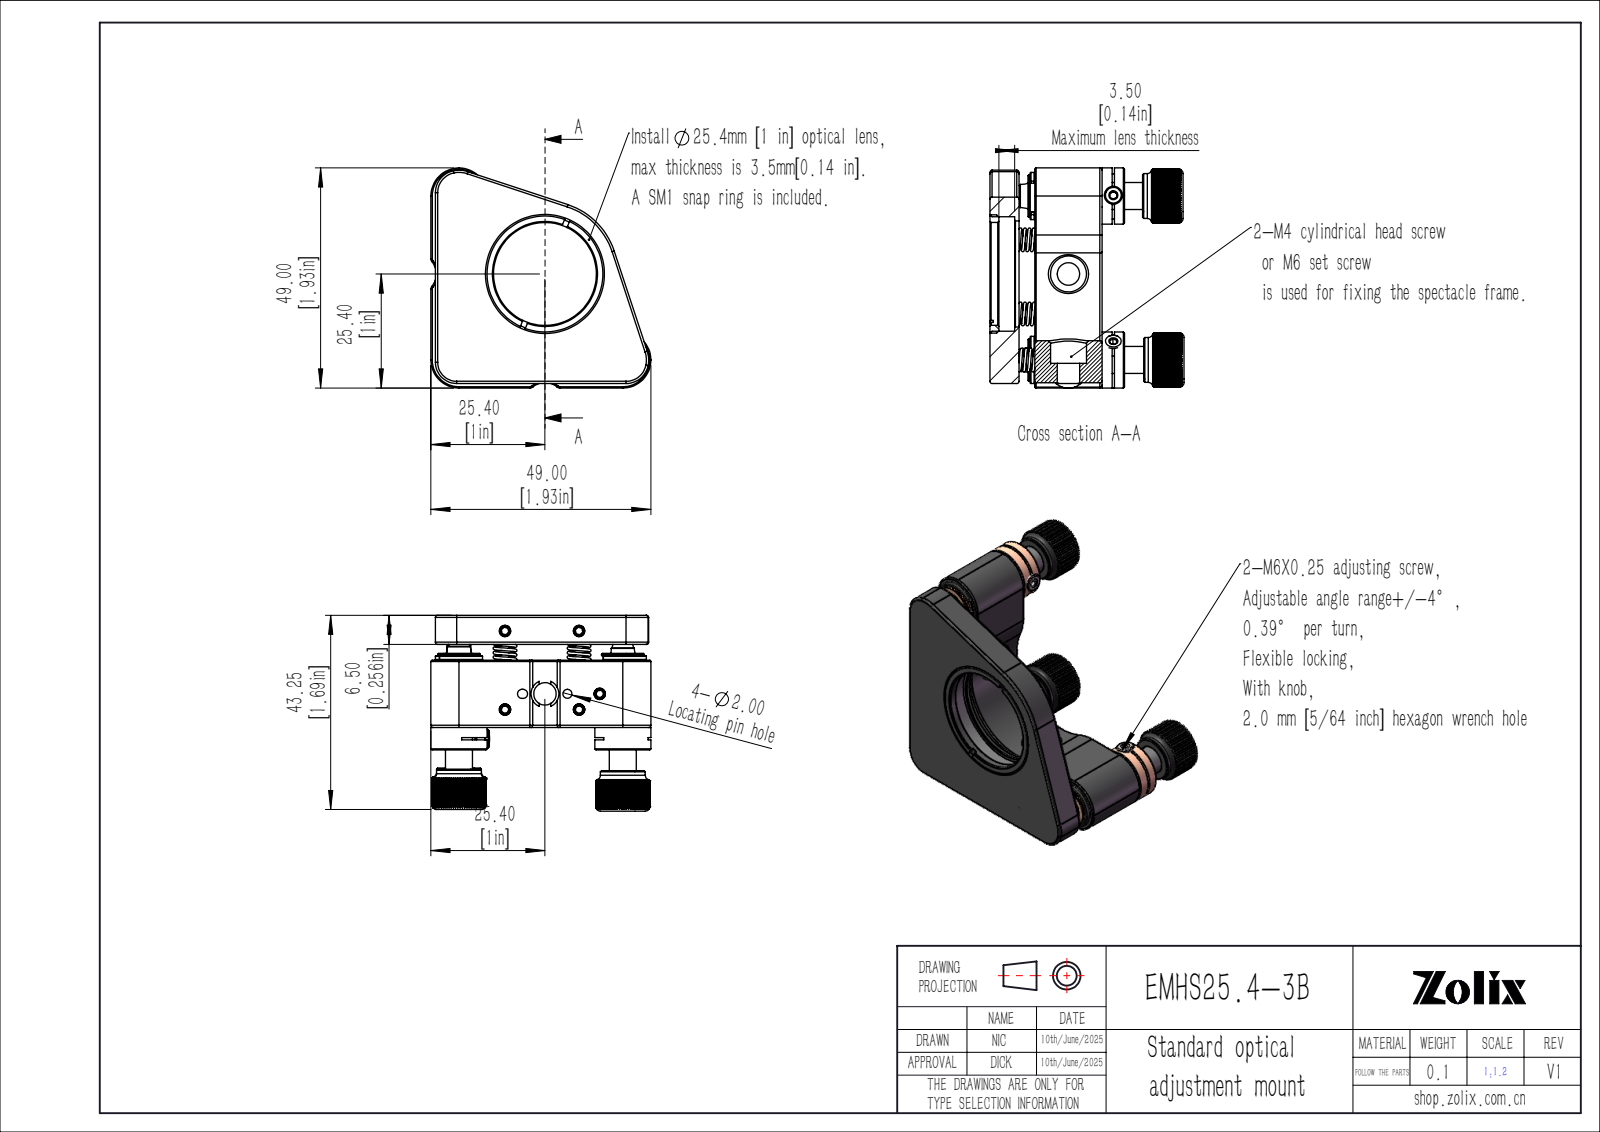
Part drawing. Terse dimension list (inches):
name: EMHS25.4-3B
written by: SolidWorks 2020 (CONFIG_CONTROL_DESIGN)
unit: in
bodies: 0 solids, 1287 faces (618 planar, 401 cylindrical, 268 other)
size: 1.929 × 1.929 × 1.717
holes: 5× ⌀0.236, 4× ⌀0.118, 2× ⌀0.394, 2× ⌀0.492, 1× ⌀0.098, 1× ⌀0.157, 1× ⌀0.181, 1× ⌀0.248, 1× ⌀0.413, 1× ⌀0.902, 1× ⌀0.929, 1× ⌀1.004
bosses: 5× ⌀0.315, 5× ⌀0.157, 4× ⌀0.118, 3× ⌀0.374, 2× ⌀0.236, 2× ⌀0.197, 2× ⌀0.079, 2× ⌀0.059
rounds: 12× R0.02, 8× R0.039, 7× R0.012, 4× R0.031, 3× R0.236, 2× R0.122, 2× R0.171, 2× R0.197
face distances: 0.256, 0.984, 0.728, 0.039, 0.138, 0.089, 0.108, 0.394, 0.02, 0.591
hole spacings: 0.65, 0.384, 0.404, 0.811, 0.831, 1.017, 1.033, 1.053
